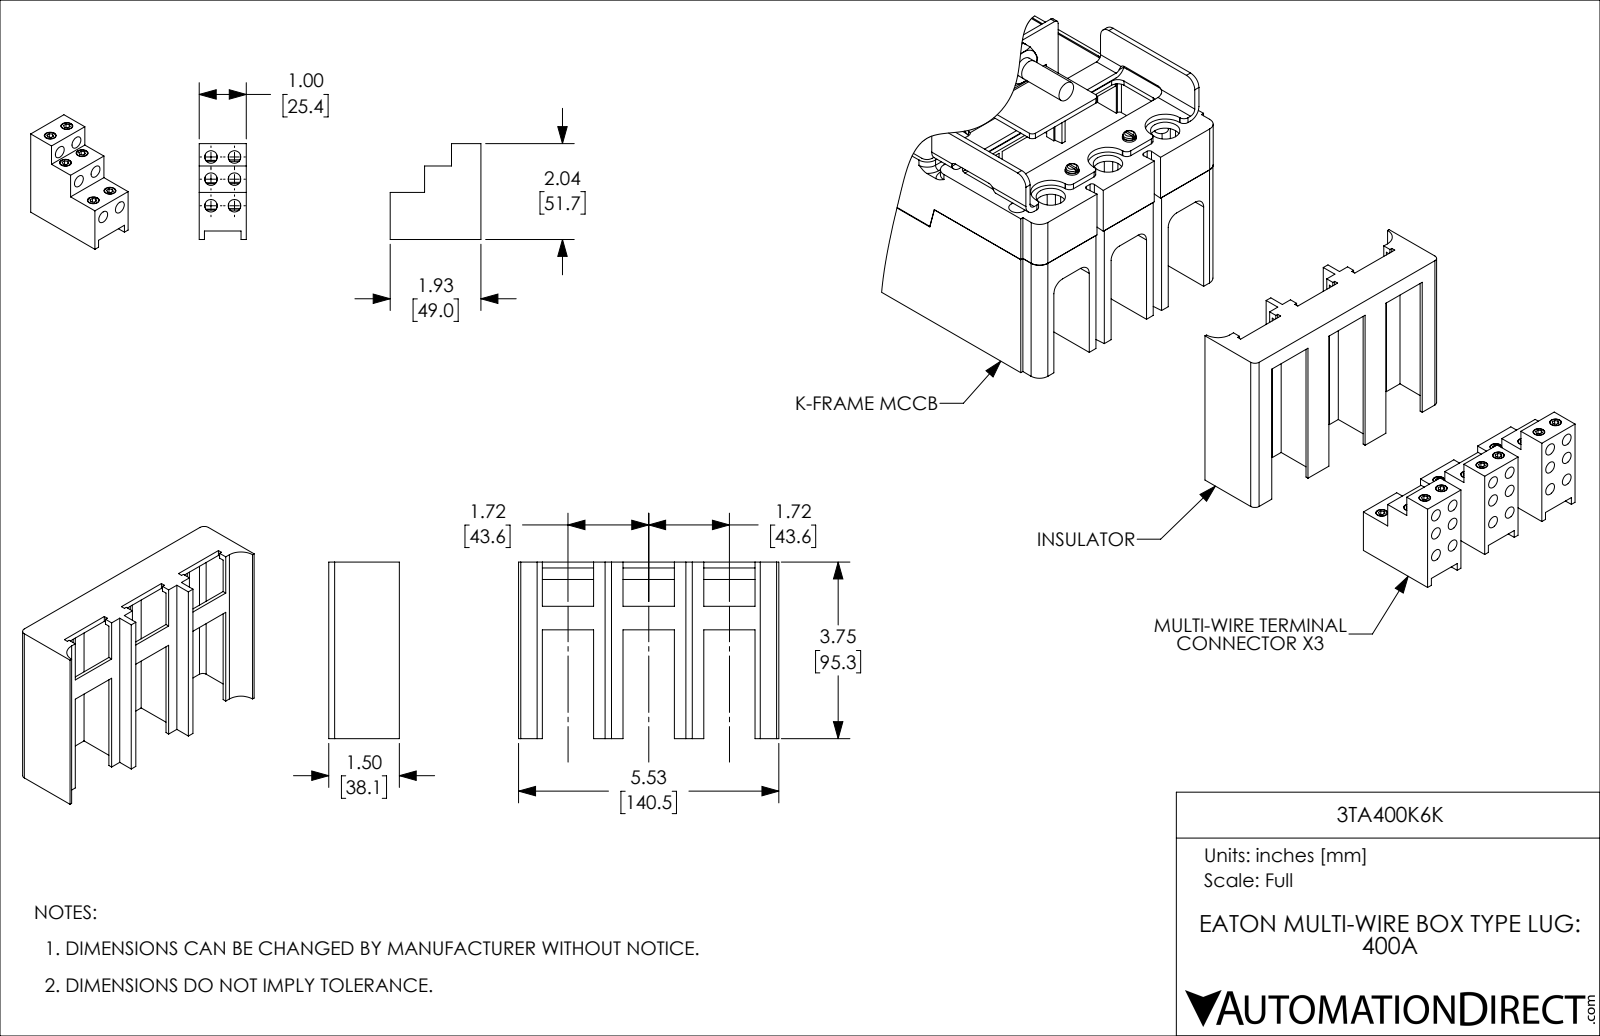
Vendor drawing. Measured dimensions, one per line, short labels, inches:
name: 3TA400K6K; 3TA400K6K_2; 3TA400K6K_1
written by: SolidWorks 2019 (CONFIG_CONTROL_DESIGN)
unit: in
bodies: 22 solids, 475 faces (283 planar, 120 cylindrical, 72 other)
size: 5.531 × 3.75 × 1.929
volume: 10.71 in³; area: 160.3 in²
holes: 18× ⌀0.25, 18× ⌀0.266, 3× ⌀0.328
rounds: 2× R0.1, 2× R0.125, 2× R0.347
face distances: 1.715, 1, 1.073, 1.952, 3.579, 0.06, 1.013, 0.1, 5.431, 1.852
hole spacings: 0.5, 1.715, 1.715, 3.43, 0.459, 0.47, 0.565, 0.678
